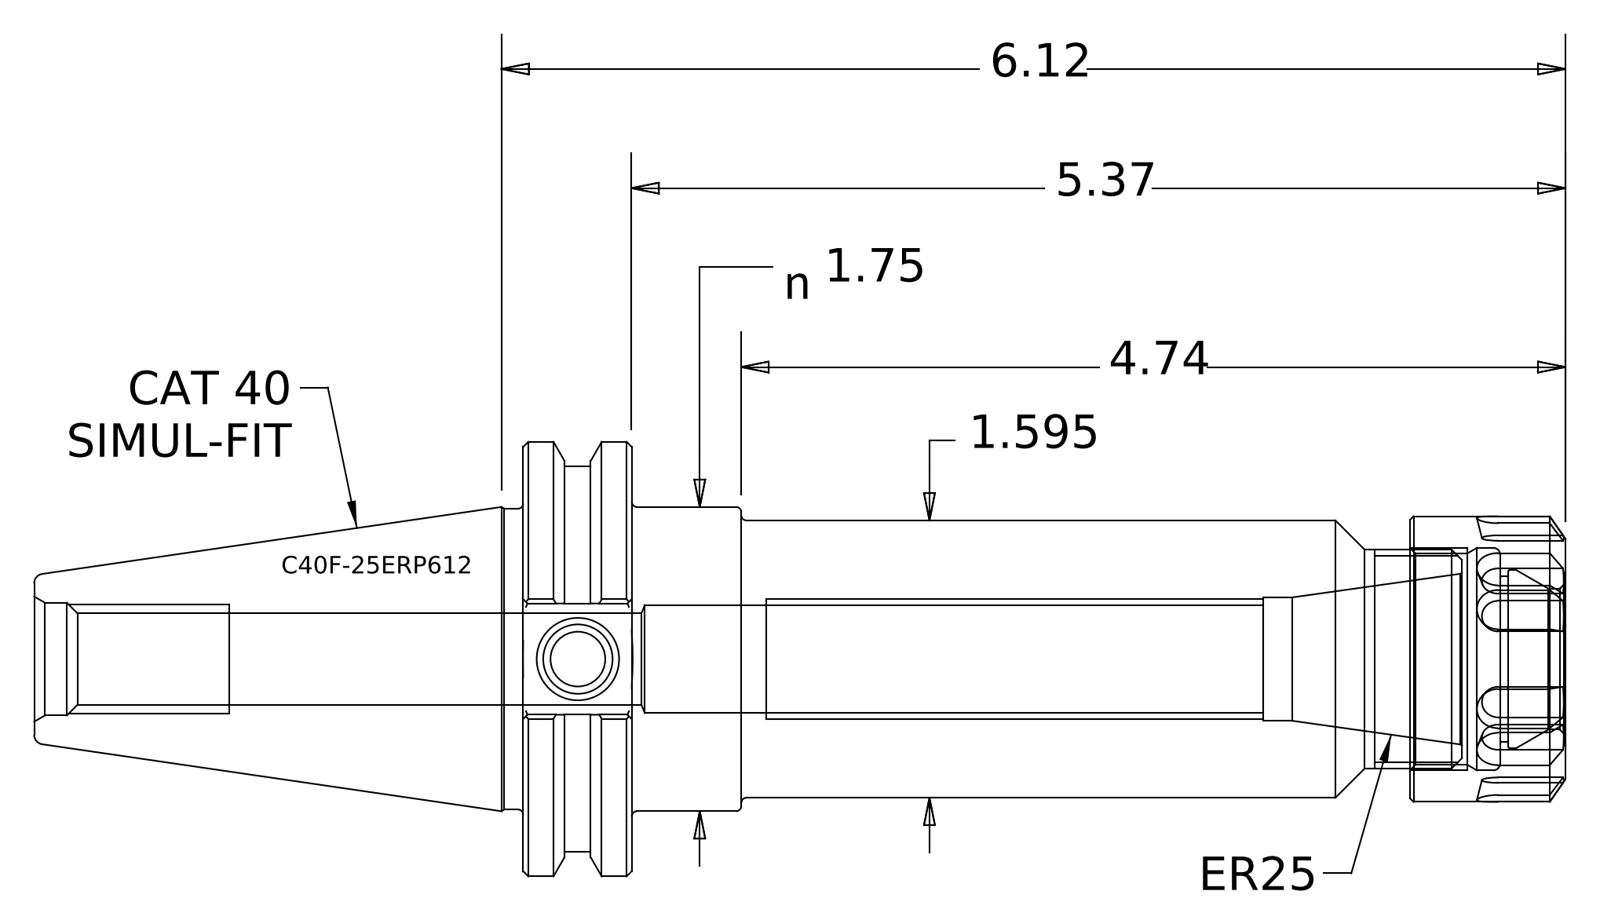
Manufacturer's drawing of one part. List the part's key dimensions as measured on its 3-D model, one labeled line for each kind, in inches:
Part name (STEP PRODUCT): C40F-25ERP612; C40F-25ER6-1; 25ERPN
STEP written by: Autodesk Inventor 2012 (AUTOMOTIVE_DESIGN)
Units: inches
Bodies: 2 solids, 133 faces (56 planar, 34 cylindrical, 43 other)
Overall size (bounding box): 8.808 × 2.5 × 2.403
Volume: 14.65 in³ · Surface area: 74.61 in²
Round holes (diameter × count): ⌀0.315 ×1, ⌀0.399 ×1, ⌀0.527 ×1, ⌀0.62 ×1, ⌀0.648 ×1, ⌀0.71 ×1, ⌀0.811 ×1, ⌀0.95 ×1, ⌀1.027 ×1, ⌀1.217 ×1, ⌀1.28 ×1
Round bosses / shafts (diameter × count): ⌀2.5 ×1, ⌀2.219 ×1, ⌀1.75 ×1, ⌀1.73 ×1, ⌀1.643 ×1, ⌀1.595 ×1, ⌀1.26 ×1
Partial cylindrical surfaces — rounded edges, fillets, slot ends (radius × count): R0.02 ×12
Main face-to-face distances: 0.625, 5.995, 5.37, 5.102, 4.477, 0.893, 5.62, 4.995, 0.518, 0.375
